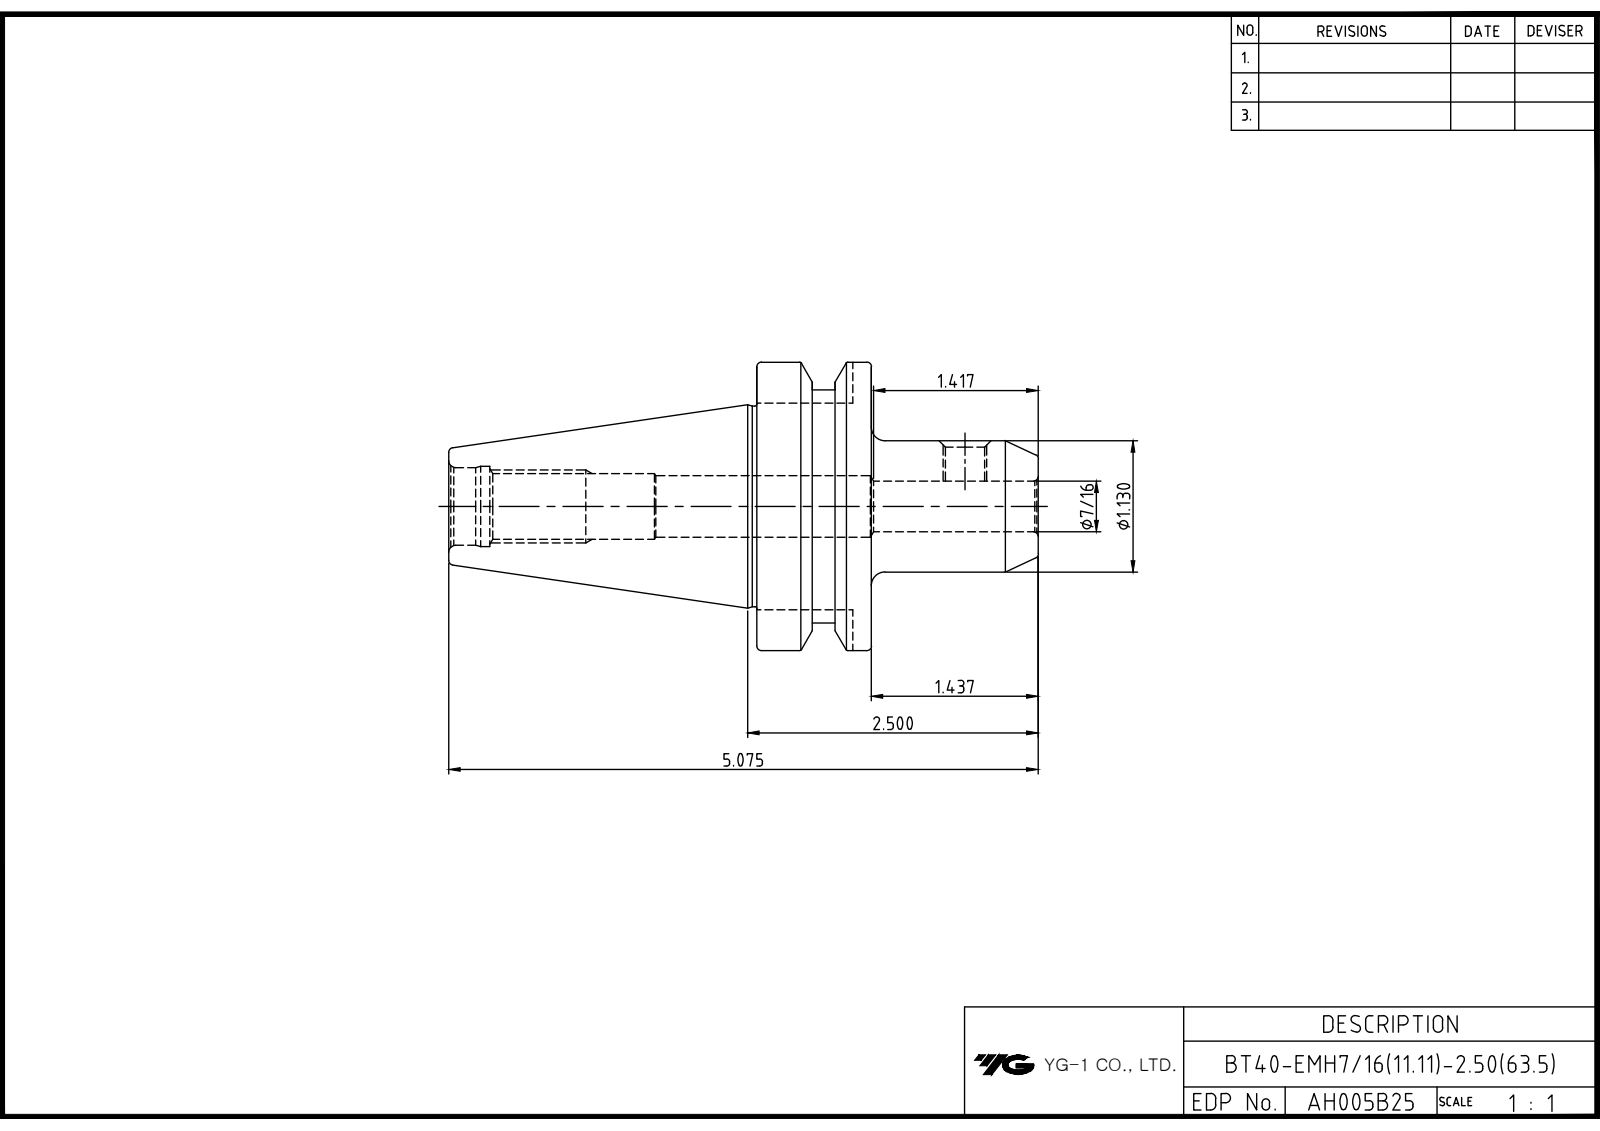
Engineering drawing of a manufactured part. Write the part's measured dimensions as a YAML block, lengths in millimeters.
part_name: "LO-BT40-EMH11.1125-63.5"
step_written_by: "Autodesk Inventor 2022 (AUTOMOTIVE_DESIGN)"
units: millimeters
bodies: {solids: 1, faces: 49, planar: 15, cylindrical: 15, other: 19}
overall_size: [128.9, 63, 63]
volume: 138522
surface_area: 26765
round_holes:
  - {diameter: 8.38, count: 1}
  - {diameter: 11.11, count: 1}
  - {diameter: 13.5, count: 1}
  - {diameter: 13.84, count: 1}
  - {diameter: 17, count: 1}
  - {diameter: 17.6, count: 1}
round_bosses_or_shafts:
  - {diameter: 63, count: 1}
  - {diameter: 52.6, count: 1}
  - {diameter: 44, count: 1}
  - {diameter: 28.7, count: 1}
partial_cylinders:
  - {radius: 8.05, count: 1}
face_to_face_distances: [25, 45.2, 61.5, 36.5, 16.1, 67.4, 92.4, 128.9, 84.5, 17.1]
